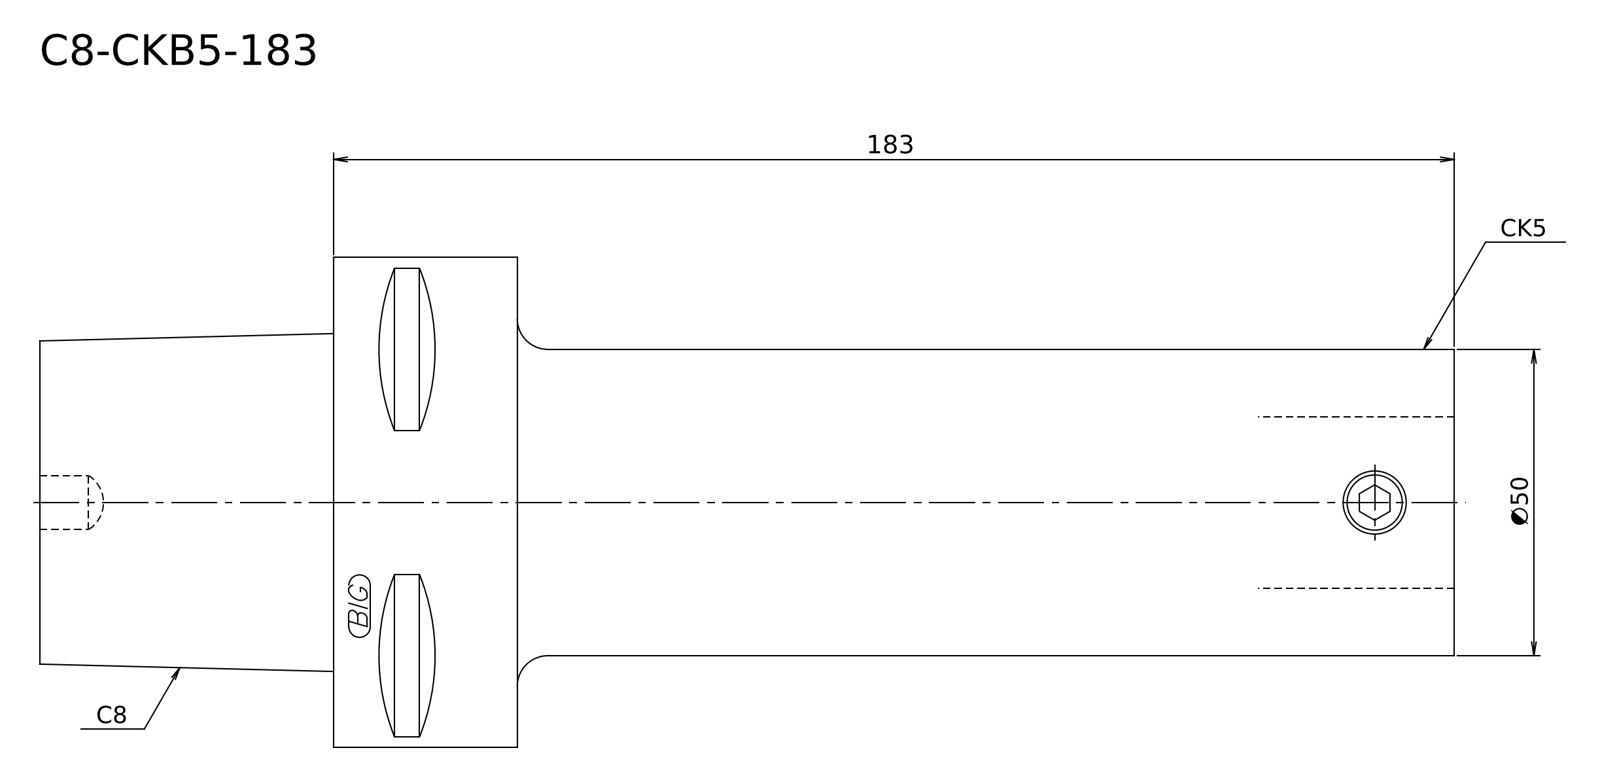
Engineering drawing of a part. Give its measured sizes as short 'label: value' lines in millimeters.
written by: Kubotek KeyCreator V8.5.1 (14335) (CONFIG_CONTROL_DESIGN)
unit: mm
bodies: 1 solid, 8 faces (4 planar, 2 cylindrical, 2 other)
size: 231 × 79.98 × 79.98
volume: 559 619 mm³; area: 49 127 mm²
bosses: 1× ⌀79.98, 1× ⌀50
face distances: 30, 78, 48, 153, 183, 231
